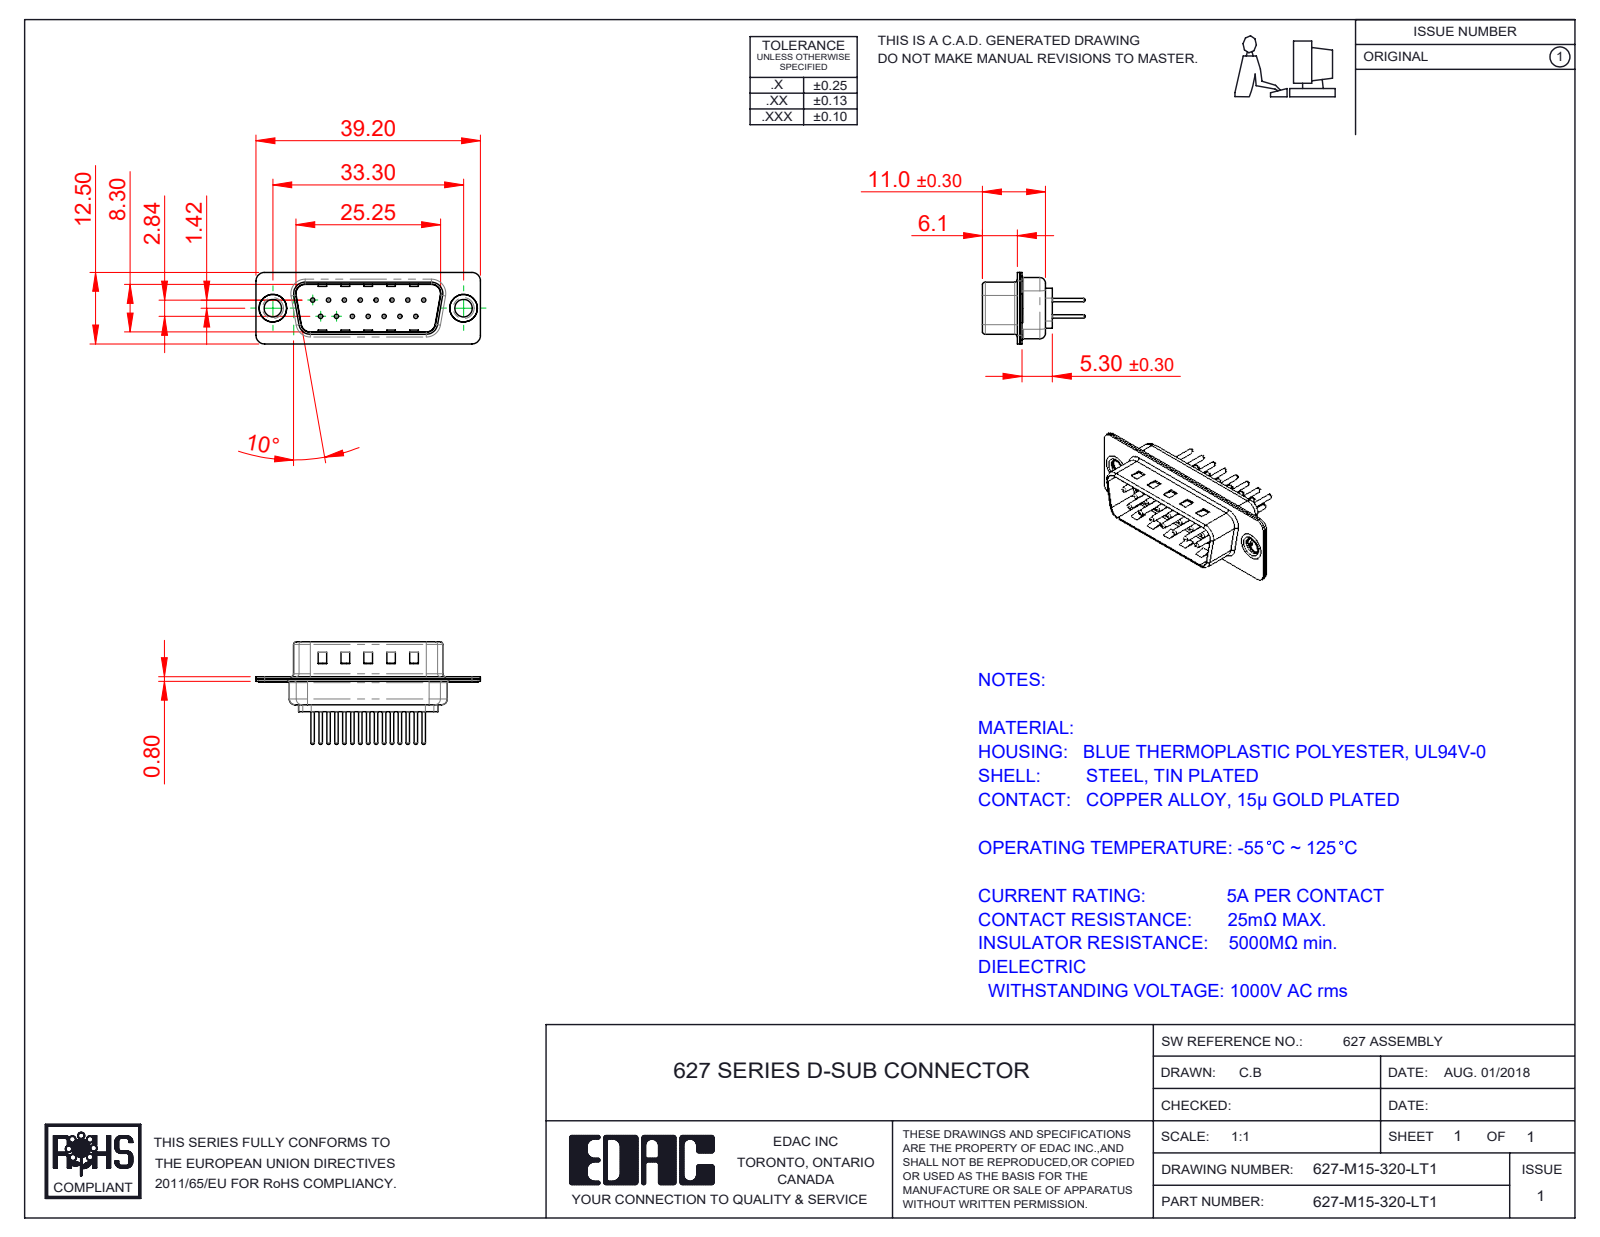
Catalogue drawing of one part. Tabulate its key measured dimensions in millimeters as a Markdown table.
| quantity | value |
| --- | --- |
| part name | 627M Contact Row 1_20; 627M Shell Rear_15 Contacts; 627M Contact Row 2_20; 627M Housing_15 Contacts (+3 more) |
| STEP written by | SolidWorks 2020 (CONFIG_CONTROL_DESIGN) |
| units | millimeters |
| bodies | 20 solids, 869 faces (244 planar, 327 cylindrical, 298 other) |
| overall size | 39.2 × 17.9 × 12.5 |
| volume | 1 765 mm³ |
| surface area | 4 663 mm² |
| round holes (diameter × count) | 0.75 × 15, 1.6 × 15, 2 × 15, 3.05 × 2, 4 × 2, 4.8 × 2 |
| round bosses / shafts (diameter × count) | 1.5 × 15, 0.6 × 15, 5 × 2, 4.9 × 2, 3.55 × 2 |
| partial cylindrical surfaces (radius × count) | 1.5 × 16, 2 × 12, 0.5 × 8, 1.6 × 8, 0.25 × 4, 0.6 × 4, 0.65 × 4, 0.9 × 4 |
| main face-to-face distances | 0.4, 0.8, 9.5, 9.1, 8.7, 9.9, 1.2, 6.1, 5.7, 5.3 |
| hole center spacings | 3.16, 2.77, 5.54, 8.31, 11.08, 5.03, 5.04, 7.48 |
